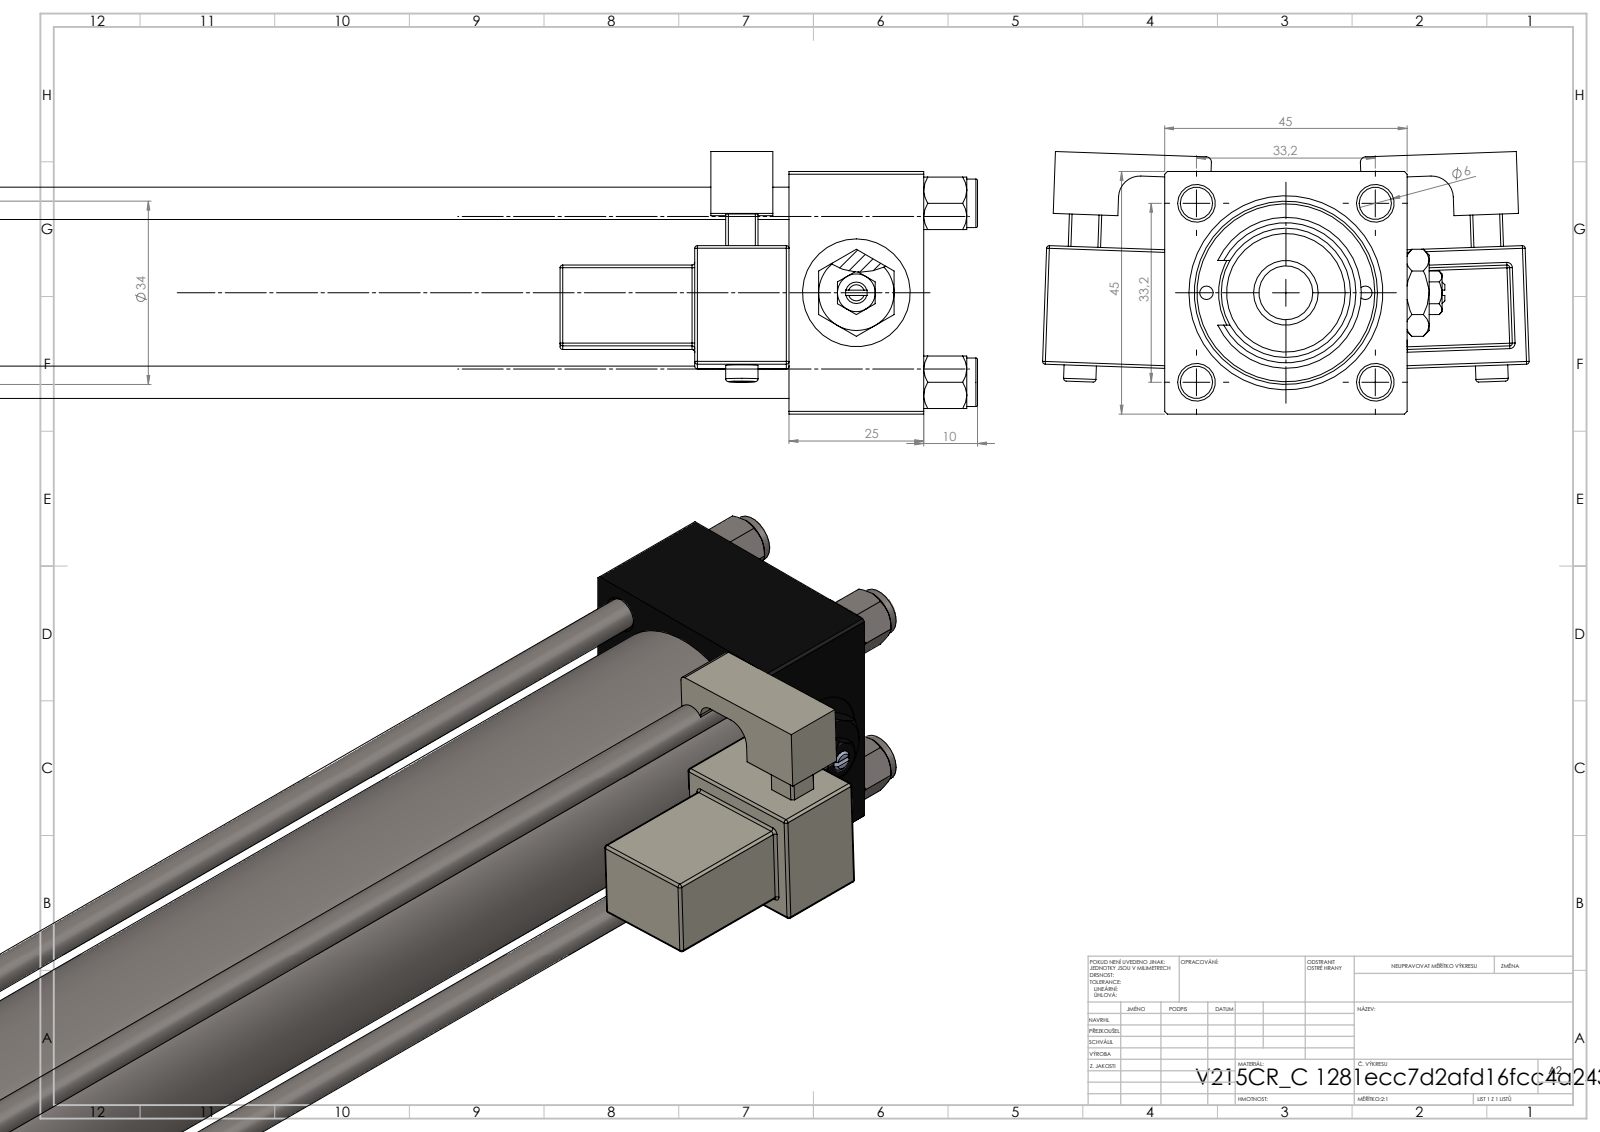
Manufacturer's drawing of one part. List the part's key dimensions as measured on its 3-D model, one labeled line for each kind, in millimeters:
Part name (STEP PRODUCT): V215CR_C_TYCINKA; V215CR_MSU; NUT_M5_C; MFA (+5 more)
STEP written by: SolidWorks 2019 (CONFIG_CONTROL_DESIGN)
Units: millimetres
Bodies: 17 solids, 1497 faces (664 planar, 175 cylindrical, 658 other)
Overall size (bounding box): 499 × 90.31 × 48.72
Volume: 497 144 mm³ · Surface area: 194 571 mm²
Round holes (diameter × count): ⌀6 ×4, ⌀2.5 ×2, ⌀7 ×2, ⌀13.16 ×2, ⌀20 ×2, ⌀10.5 ×1, ⌀22 ×1, ⌀24 ×1, ⌀25 ×1, ⌀32 ×1, ⌀33 ×1
Round bosses / shafts (diameter × count): ⌀9 ×4, ⌀6 ×2, ⌀38 ×1, ⌀34 ×1, ⌀28 ×1, ⌀18 ×1, ⌀12 ×1, ⌀11 ×1
Partial cylindrical surfaces — rounded edges, fillets, slot ends (radius × count): R0.5 ×48, R1 ×2, R2.5 ×2, R4 ×2, R9.75 ×1, R10.5 ×1
Main face-to-face distances: 45, 25, 3, 355, 330, 403, 22.99, 44.8, 14.5, 13
Hole centre spacings: 16.7, 23.48, 33.2, 35.47, 14.75, 46.95, 29.5, 355.5
